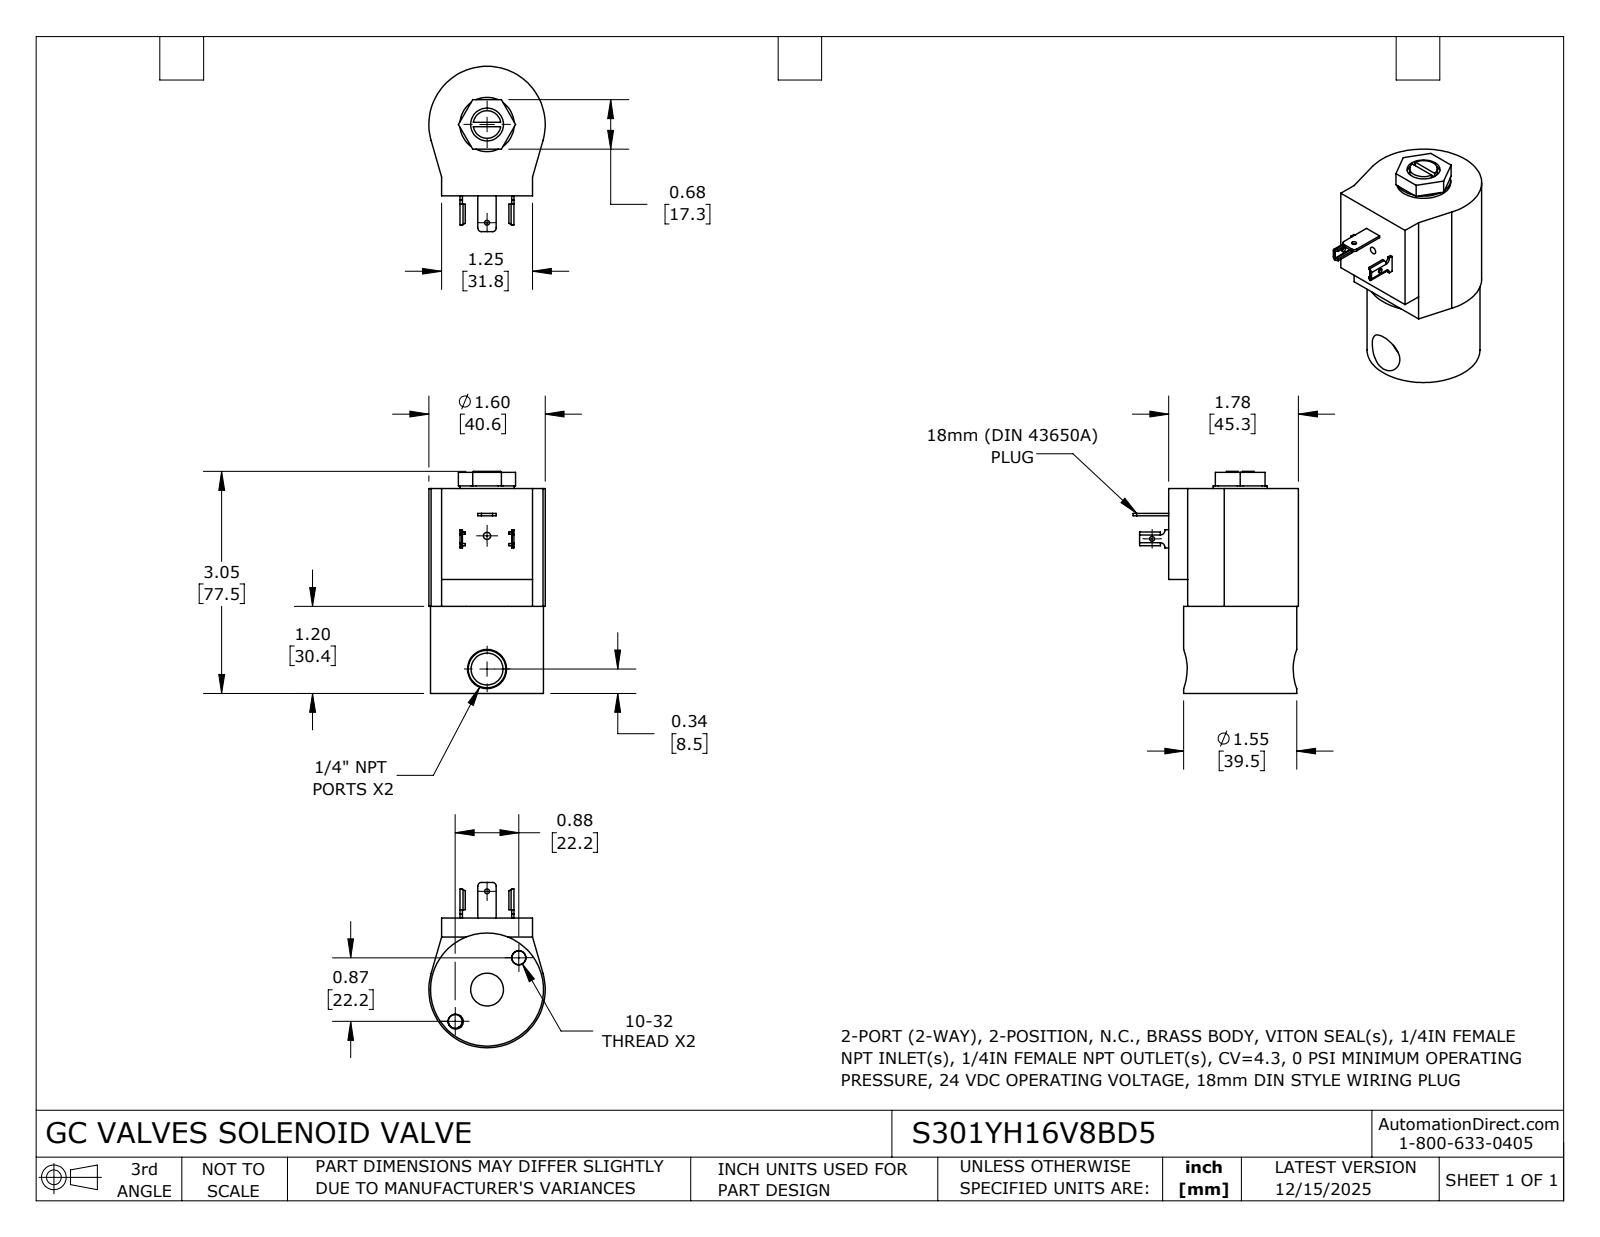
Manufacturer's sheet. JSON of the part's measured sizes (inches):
{"part_name": "S301YH16V8BD5", "step_written_by": "SolidWorks 2024 (CONFIG_CONTROL_DESIGN)", "units": "inches", "bodies": {"solids": 2, "faces": 171, "planar": 78, "cylindrical": 71, "other": 22}, "overall_size": [3.061, 2.273, 1.6], "volume_in3": 5.834, "surface_area_in2": 27.56, "round_holes": [[0.19, 2], [0.066, 1], [0.067, 1], [0.1, 1], [0.438, 1], [0.451, 1]], "round_bosses_or_shafts": [[1.553, 1], [0.746, 1], [0.38, 1]], "partial_cylinders_radius": [[0.006, 4], [0.041, 4], [0.05, 2], [0.06, 2], [0.8, 1]], "face_to_face_distances": [1.62, 1.195, 2.815, 0.26, 1.565, 0.37, 1.25, 1.25, 3.038, 1.843], "hole_center_spacings": [0.618, 0.619, 1.012, 1.237, 1.35, 1.83, 1.84]}
